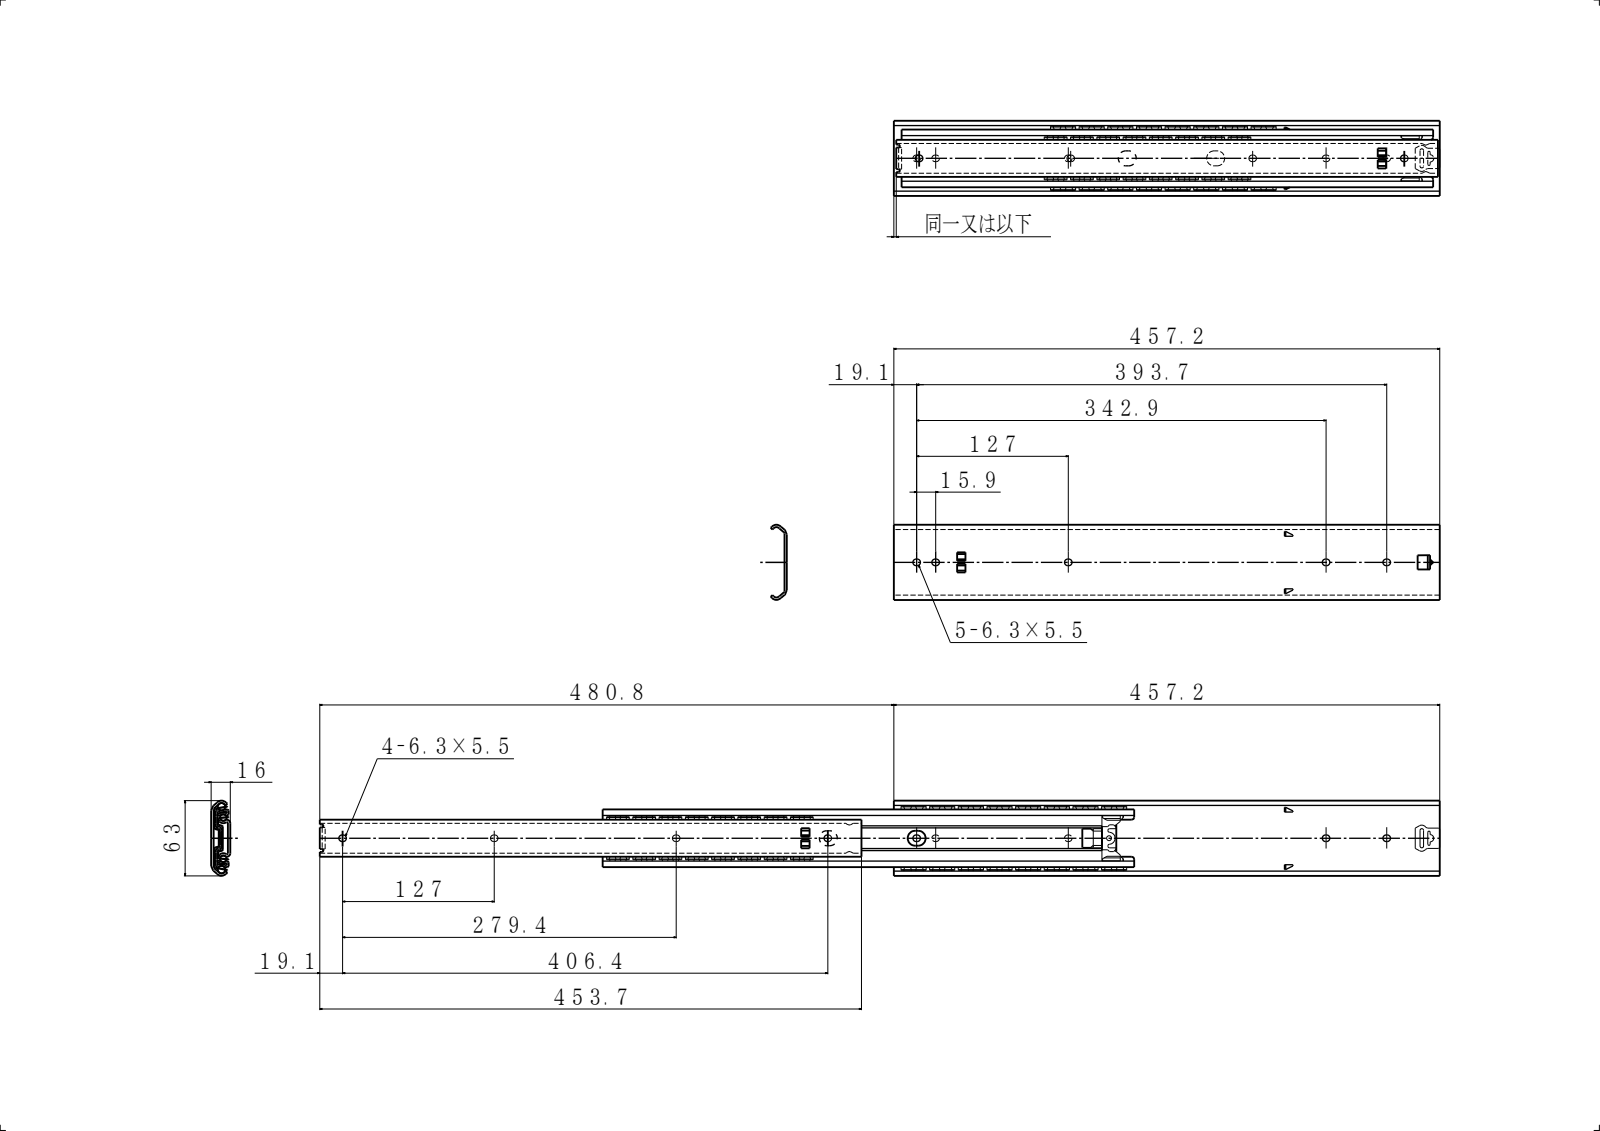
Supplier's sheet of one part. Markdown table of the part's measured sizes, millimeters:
| quantity | value |
| --- | --- |
| part name | C630-18 OM; PN160A; C630-18; C630-18 IM (+5 more) |
| STEP written by | SolidWorks 2019 (CONFIG_CONTROL_DESIGN) |
| units | millimeters |
| bodies | 10 solids, 634 faces (392 planar, 240 cylindrical, 2 other) |
| overall size | 938.54 × 63 × 16 |
| volume | 182 727 mm³ |
| surface area | 207 444 mm² |
| round holes (diameter × count) | 5.4 × 1 |
| round bosses / shafts (diameter × count) | 5 × 1 |
| partial cylindrical surfaces (radius × count) | 1 × 22, 0.5 × 20, 2.75 × 18, 2 × 16, 0.3 × 12, 1.2 × 10, 0.2 × 8, 1.6 × 8 |
| main face-to-face distances | 2, 14, 1.56, 12, 16, 4.08, 1.3, 12.7, 2.86, 11.14 |
